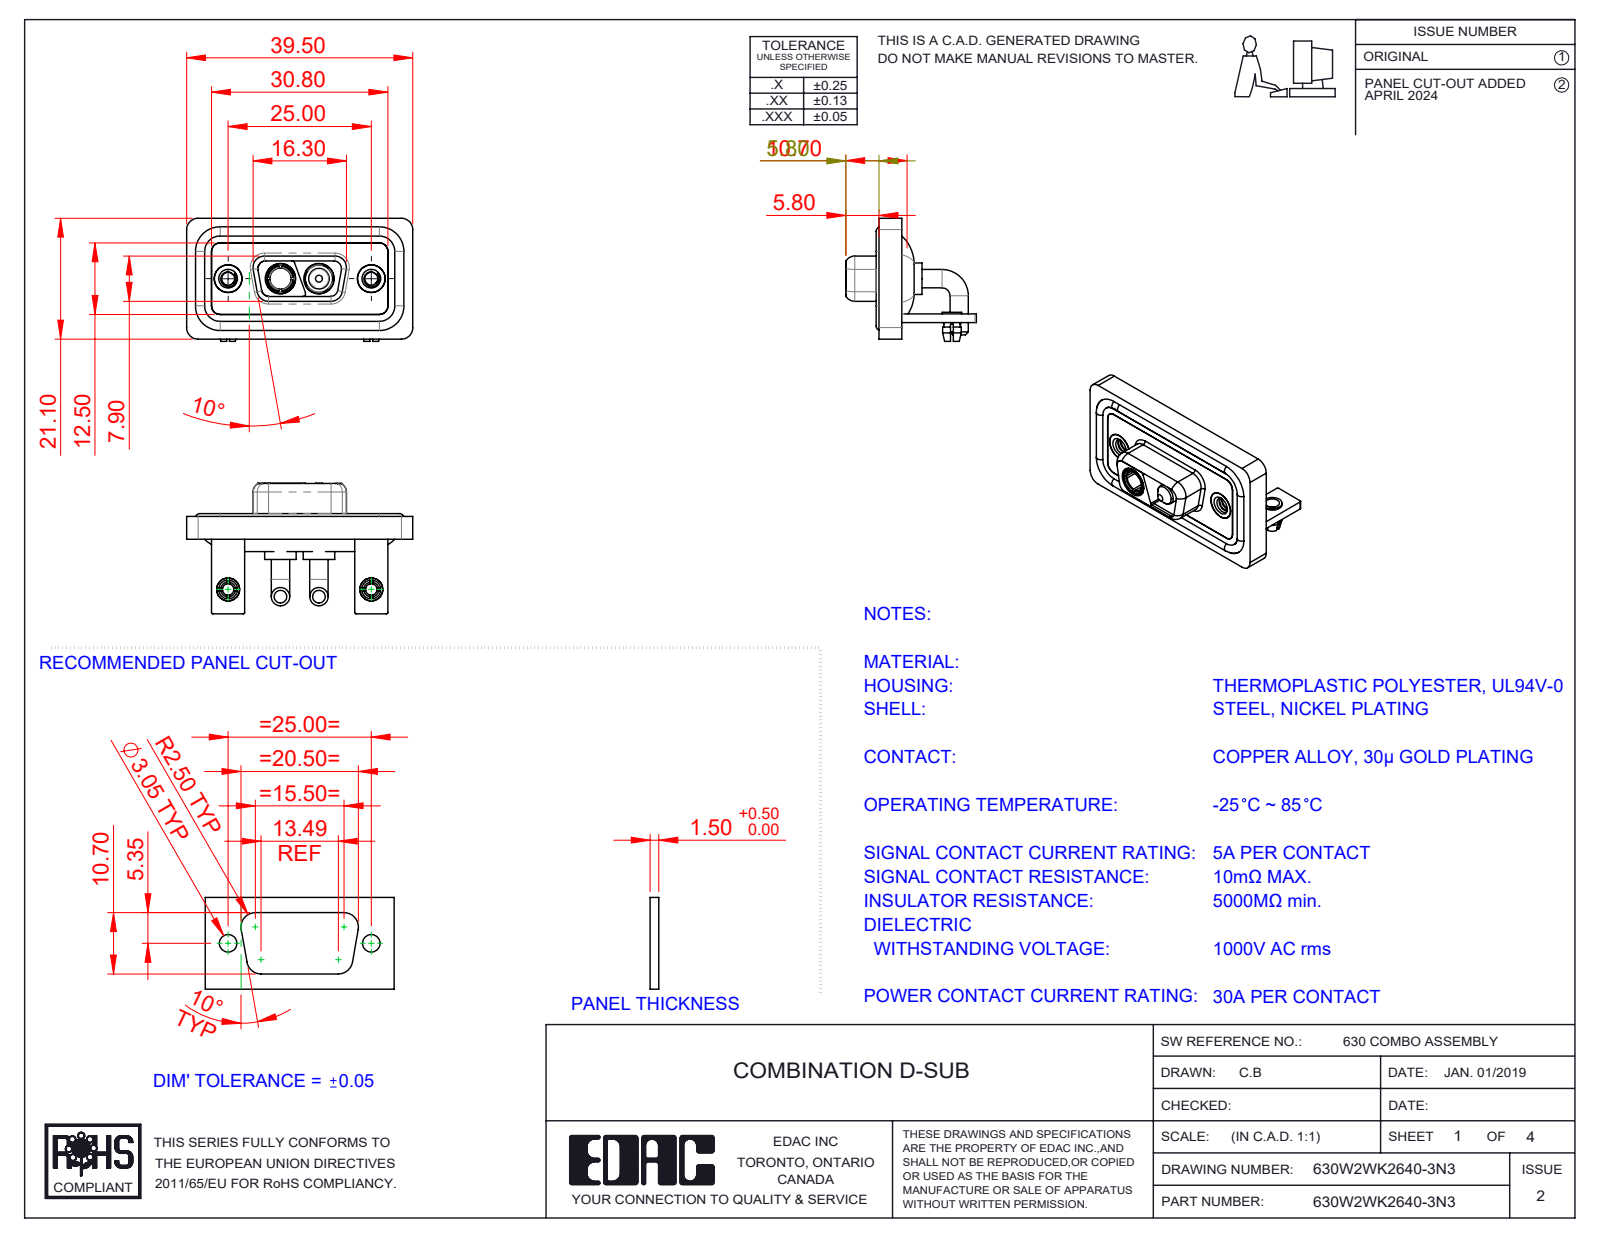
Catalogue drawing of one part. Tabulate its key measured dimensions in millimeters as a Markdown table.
| quantity | value |
| --- | --- |
| part name | 630Combo Shell Front_09 Contacts; Power Pin_30A RA; 630Combo Housing_2WK2; 630Combo Threaded Rivet_2 (+6 more) |
| STEP written by | SolidWorks 2023 (CONFIG_CONTROL_DESIGN) |
| units | millimeters |
| bodies | 15 solids, 648 faces (212 planar, 291 cylindrical, 145 other) |
| overall size | 39.5 × 22.8 × 21.5 |
| volume | 5 165 mm³ |
| surface area | 8 477 mm² |
| round holes (diameter × count) | 4.85 × 4, 2 × 2, 2.26 × 2, 2.5 × 2, 3.2 × 2, 4 × 2, 4.05 × 2, 5 × 2, 5.3 × 2, 3.7 × 1 |
| round bosses / shafts (diameter × count) | 3.2 × 4, 1.6 × 4, 5.5 × 2, 5.2 × 2, 4.95 × 2, 4.8 × 2, 4.75 × 2, 4 × 2 |
| partial cylindrical surfaces (radius × count) | 2 × 19, 1.5 × 18, 0.25 × 16, 1.35 × 8, 1.6 × 8, 0.5 × 7, 0.6 × 4, 0.65 × 4 |
| main face-to-face distances | 0.4, 2.9, 1.5, 1.1, 3.7, 1.8, 0.8, 2.5, 1.6, 3.1 |
| hole center spacings | 9.14, 15.86, 25, 6.72 |
